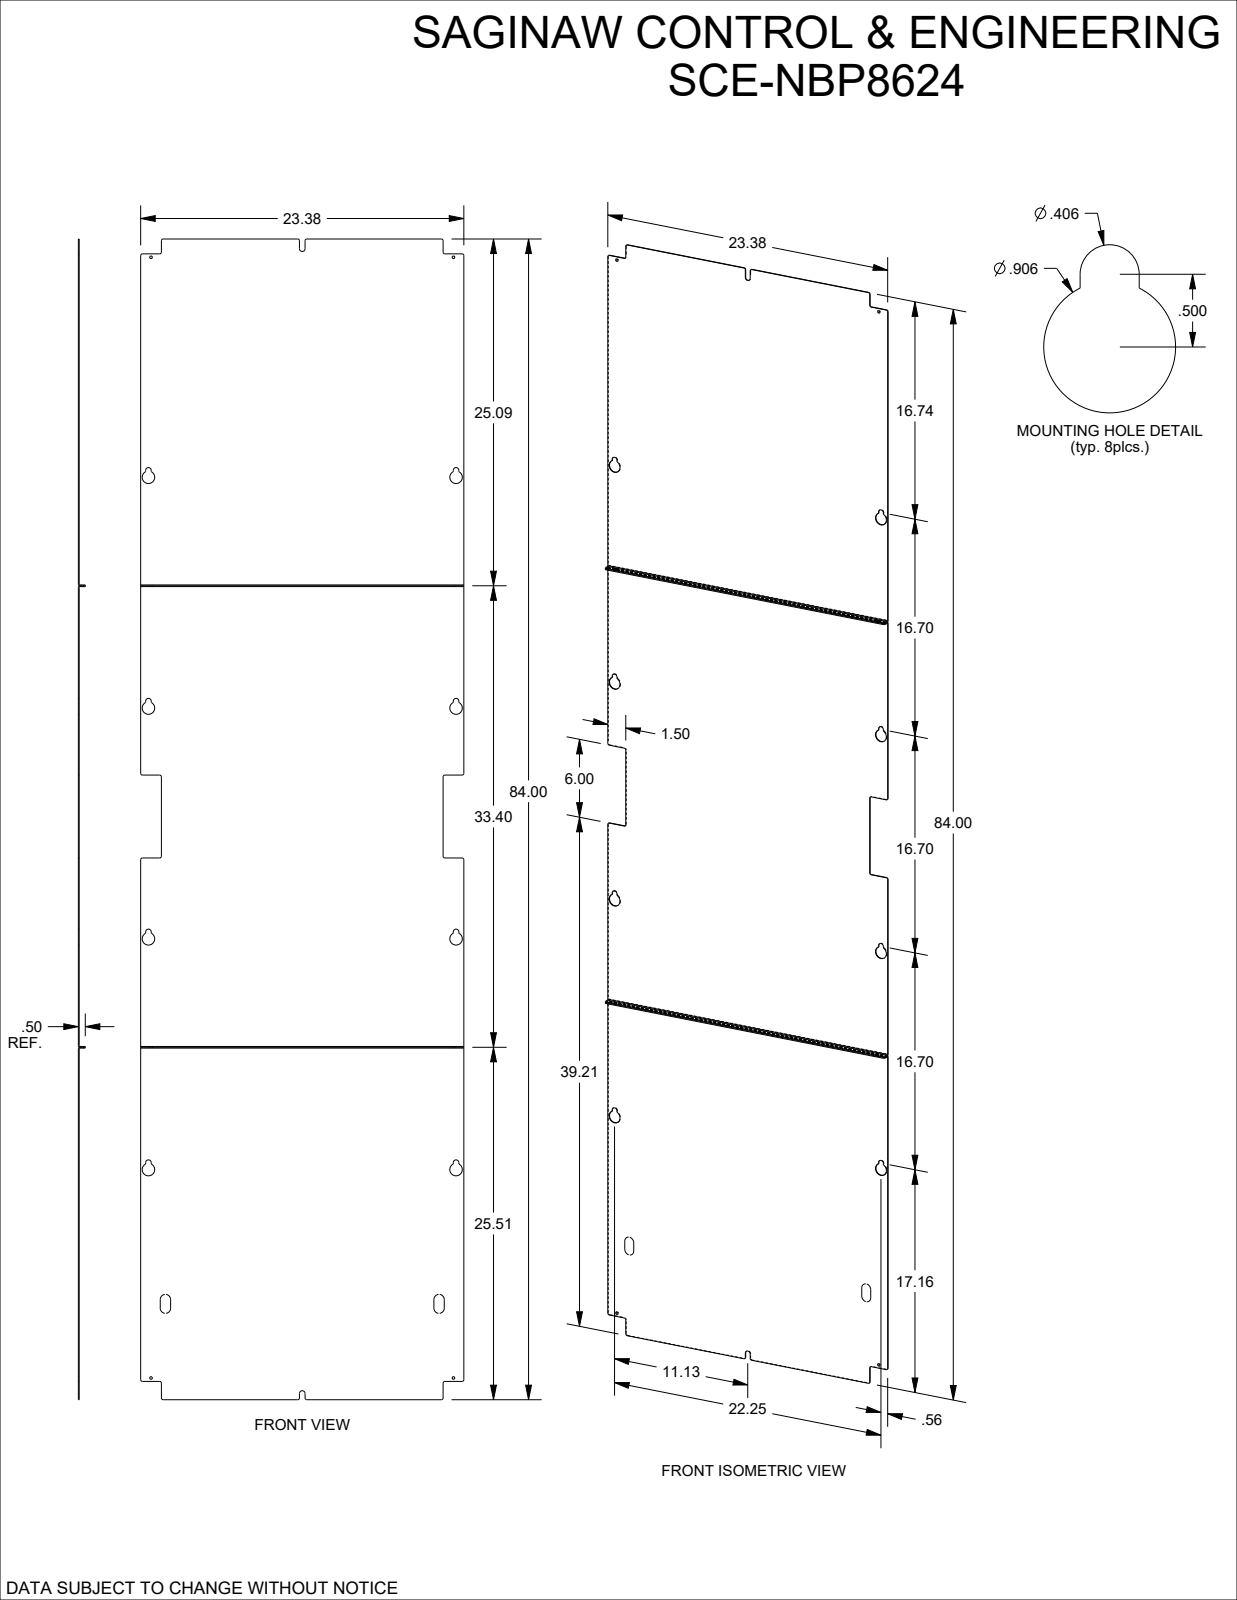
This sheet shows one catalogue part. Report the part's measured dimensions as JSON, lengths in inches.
{"part_name": "SCE-NBP8624", "step_written_by": "SolidWorks 2023 (AUTOMOTIVE_DESIGN)", "units": "inches", "bodies": {"solids": 3, "faces": 174, "planar": 80, "cylindrical": 94, "other": 0}, "overall_size": [84, 23.375, 0.5], "volume_in3": 118.2, "surface_area_in2": 3960, "round_holes": [[0.906, 8], [0.188, 6]], "partial_cylinders_radius": [[0.125, 26], [0.03, 12], [0.203, 10], [0.052, 4], [0.112, 4]], "face_to_face_distances": [0.06, 33.4, 33.46, 0.12, 33.34, 33.52, 33.28, 0.44, 0.5, 23.375], "hole_center_spacings": [16.7, 27.82, 22.25, 33.4, 40.133, 21.875, 15.081, 15.921]}
